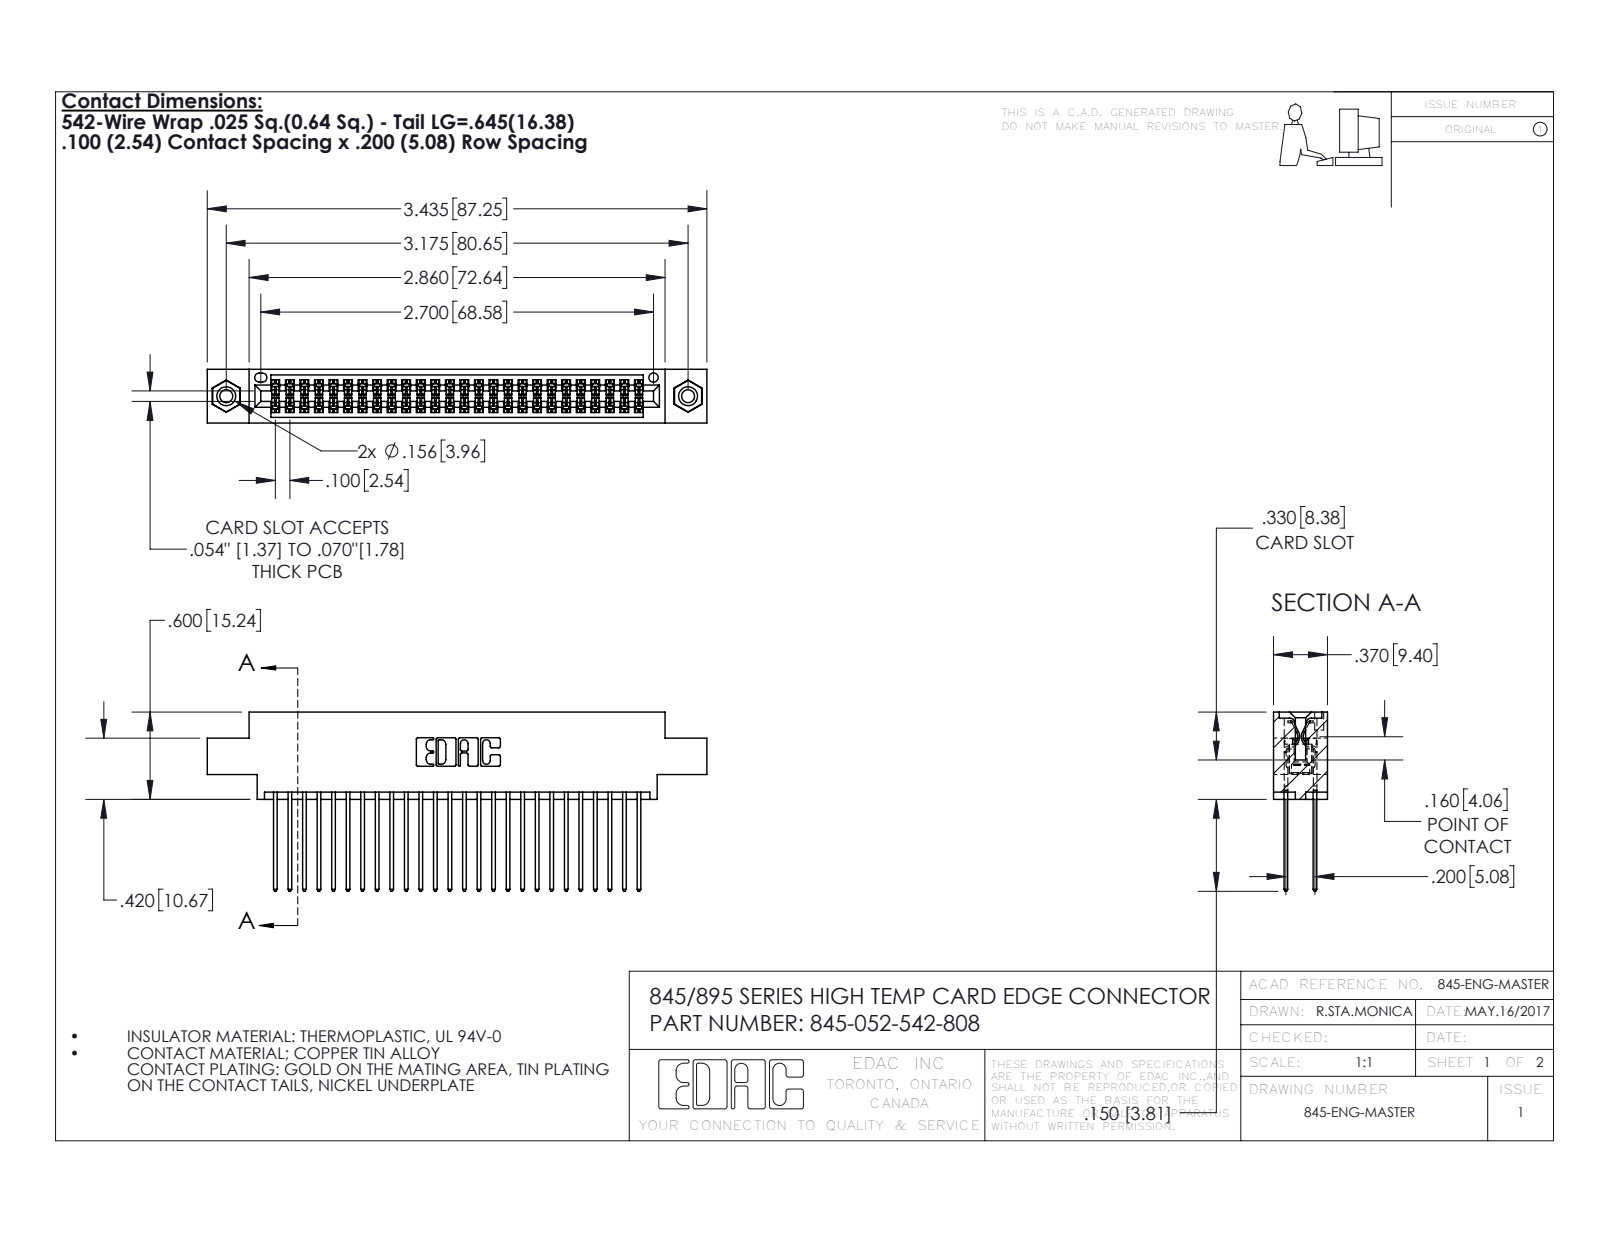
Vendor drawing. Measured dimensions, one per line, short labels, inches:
name: 345-292-001_345-293-142; 345 Part_0.170 Offset - 0.156 Dia-TI; 345-052-542-808; 345-250-001_345-250-003-102
written by: SolidWorks 2016 (CONFIG_CONTROL_DESIGN)
unit: in
bodies: 31 solids, 1782 faces (1208 planar, 558 cylindrical, 16 other)
size: 3.435 × 1.232 × 0.37
volume: 0.496 in³; area: 17.42 in²
holes: 2× ⌀0.089, 2× ⌀0.125, 2× ⌀0.156, 1× ⌀0.064
bosses: 2× ⌀0.155
rounds: 54× R0.006, 52× R0.01, 22× R0.01, 6× R0.007, 6× R0.031, 3× R0.026, 2× R0.014, 2× R0.019
face distances: 0.072, 0.298, 0.37, 0.2, 0.098, 0.272, 0.025, 0.225, 0.175, 0.149
hole spacings: 0.27, 2.94, 3.175
